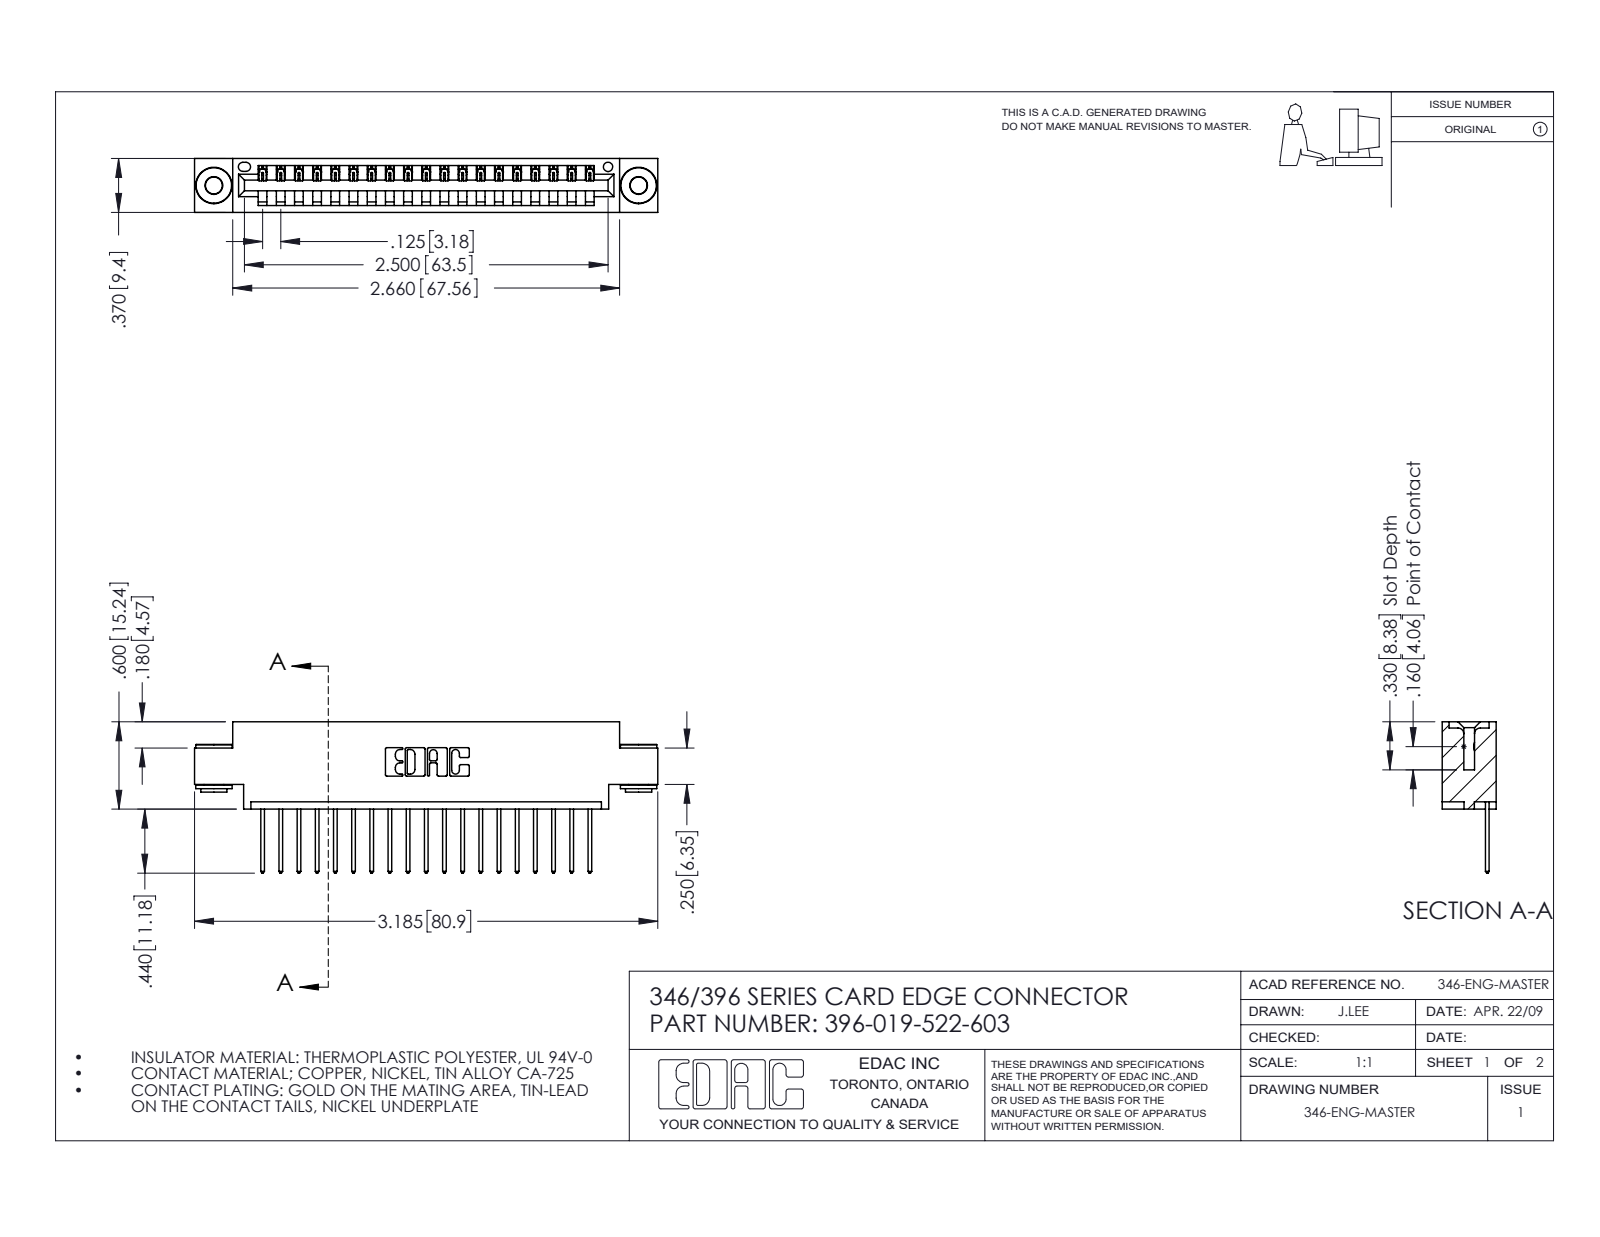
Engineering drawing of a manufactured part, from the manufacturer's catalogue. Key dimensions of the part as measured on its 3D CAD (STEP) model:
Part name (STEP PRODUCT): 346 Part_0.170 Offset - 0.156 Dia-TH; 396-019-522-603; 345-292-001_345-293-122; 345-250-002_345-250-002-102
STEP written by: SolidWorks 2016 (CONFIG_CONTROL_DESIGN)
Units: inches
Bodies: 22 solids, 1266 faces (850 planar, 408 cylindrical, 8 other)
Overall size (bounding box): 3.185 × 1.04 × 0.37
Volume: 0.455 in³ · Surface area: 14.75 in²
Round holes (diameter × count): ⌀0.116 ×2, ⌀0.156 ×2, ⌀0.064 ×1
Round bosses / shafts (diameter × count): ⌀0.25 ×2, ⌀0.18 ×2, ⌀0.136 ×2
Partial cylindrical surfaces — rounded edges, fillets, slot ends (radius × count): R0.006 ×38, R0.01 ×38, R0.01 ×22, R0.007 ×6, R0.031 ×6, R0.026 ×3, R0.031 ×2, R0.04 ×2
Main face-to-face distances: 0.048, 0.322, 0.37, 0.25, 0.025, 0.072, 0.298, 0.148, 0.222, 0.1
Hole centre spacings: 0.246, 2.713, 2.92
